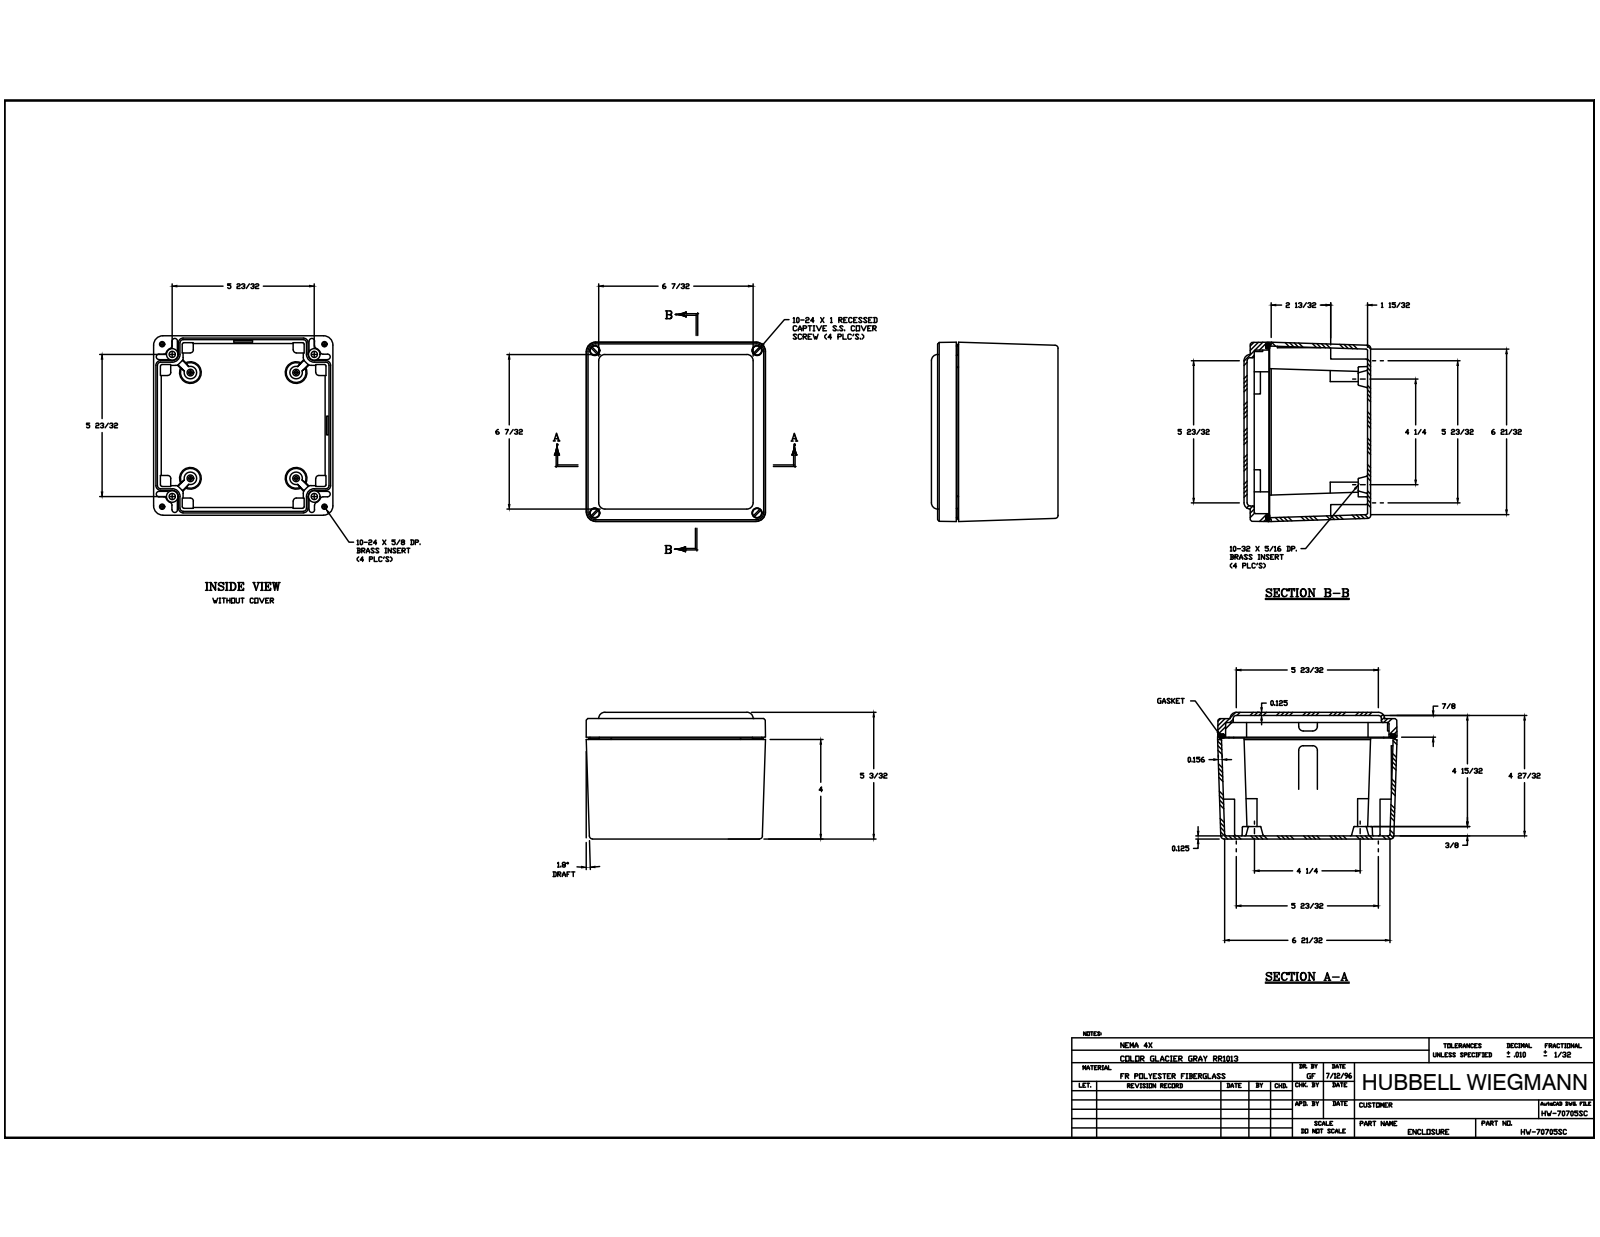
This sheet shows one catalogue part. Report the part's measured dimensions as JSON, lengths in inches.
{"part_name": "WP707WBOX; 0.3125-18 X 0.563 DP BRASS INSERT; 10-32 X0.3125 DP BRASS INSERT; 10-24 X 0.625 DP BRASS INSERT (+5 more)", "step_written_by": "Autodesk Inventor 2014 (AUTOMOTIVE_DESIGN)", "units": "inches", "bodies": {"solids": 23, "faces": 1078, "planar": 426, "cylindrical": 260, "other": 392}, "overall_size": [7.22, 7.22, 5.094], "volume_in3": 49.84, "surface_area_in2": 549.6, "round_holes": [[0.281, 8], [0.145, 4], [0.156, 4], [0.156, 4], [0.19, 4], [0.219, 4], [0.23, 4], [0.28, 4], [0.313, 4], [0.406, 4], [0.531, 4]], "round_bosses_or_shafts": [[0.375, 4], [0.364, 4], [0.191, 4]], "partial_cylinders_radius": [[0.031, 49], [0.125, 30], [0.063, 29], [0.01, 16], [0.059, 8], [0.375, 8], [0.187, 6], [0.25, 4]], "face_to_face_distances": [0.186, 0.125, 4.844, 5.094, 4.969, 0.125, 4.969, 4.094, 0.75, 0.25], "hole_center_spacings": [5.04, 5.511, 5.511, 6.139, 6.14, 6.532, 0.574, 0.574]}
